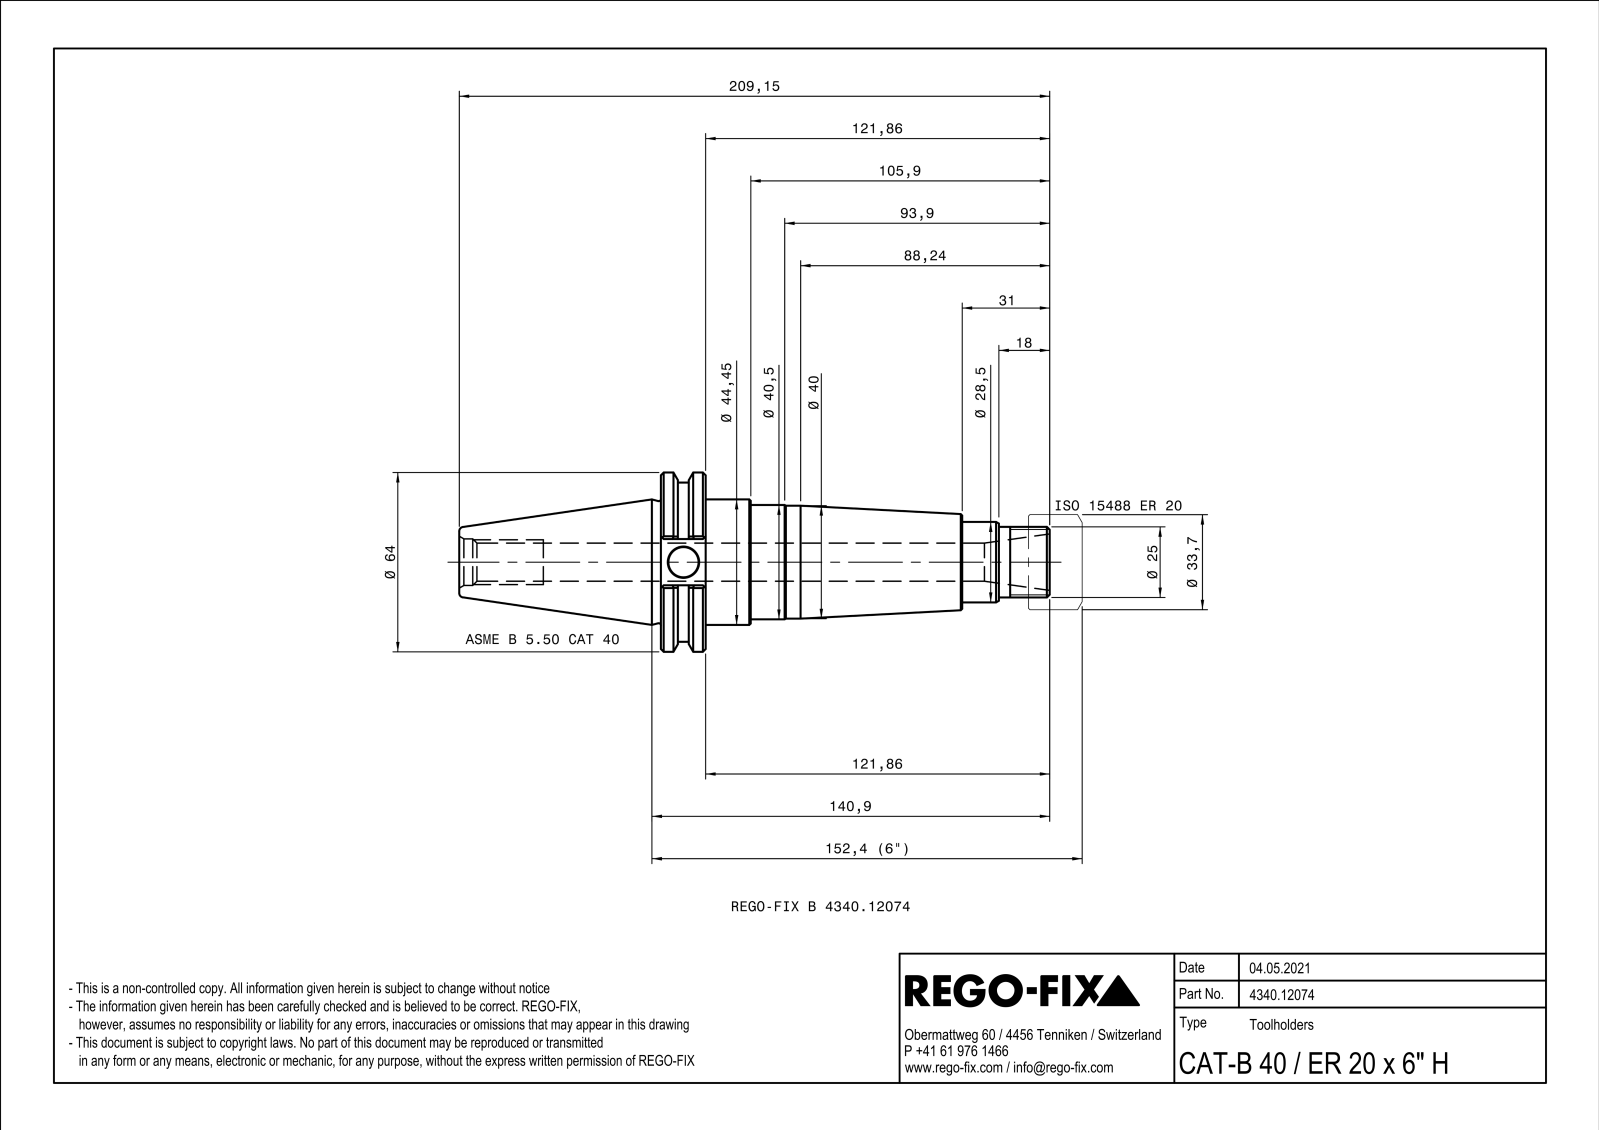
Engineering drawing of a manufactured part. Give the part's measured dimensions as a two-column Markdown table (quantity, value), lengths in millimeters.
| quantity | value |
| --- | --- |
| part name | NOCUT |
| STEP written by | SIEMENS PLM Software Solid Edge ST10 (AUTOMOTIVE_DESIGN) |
| units | millimeters |
| bodies | 1 solid, 130 faces (33 planar, 36 cylindrical, 61 other) |
| overall size | 209.15 × 63.5 × 60.79 |
| volume | 205 546 mm³ |
| surface area | 39 347 mm² |
| round holes (diameter × count) | 3.24 × 2, 3.9 × 2, 10.7 × 1, 13.5 × 1, 13.53 × 1, 16.5 × 1 |
| round bosses / shafts (diameter × count) | 63.5 × 1, 56.36 × 1, 44.45 × 1, 40.5 × 1, 40 × 1, 28.5 × 1, 25 × 1 |
| partial cylindrical surfaces (radius × count) | 0.5 × 4 |
| main face-to-face distances | 15.87, 90.86, 106.73, 47.33, 16.38, 74.9, 15.96, 31.83, 178.15, 103.25 |
